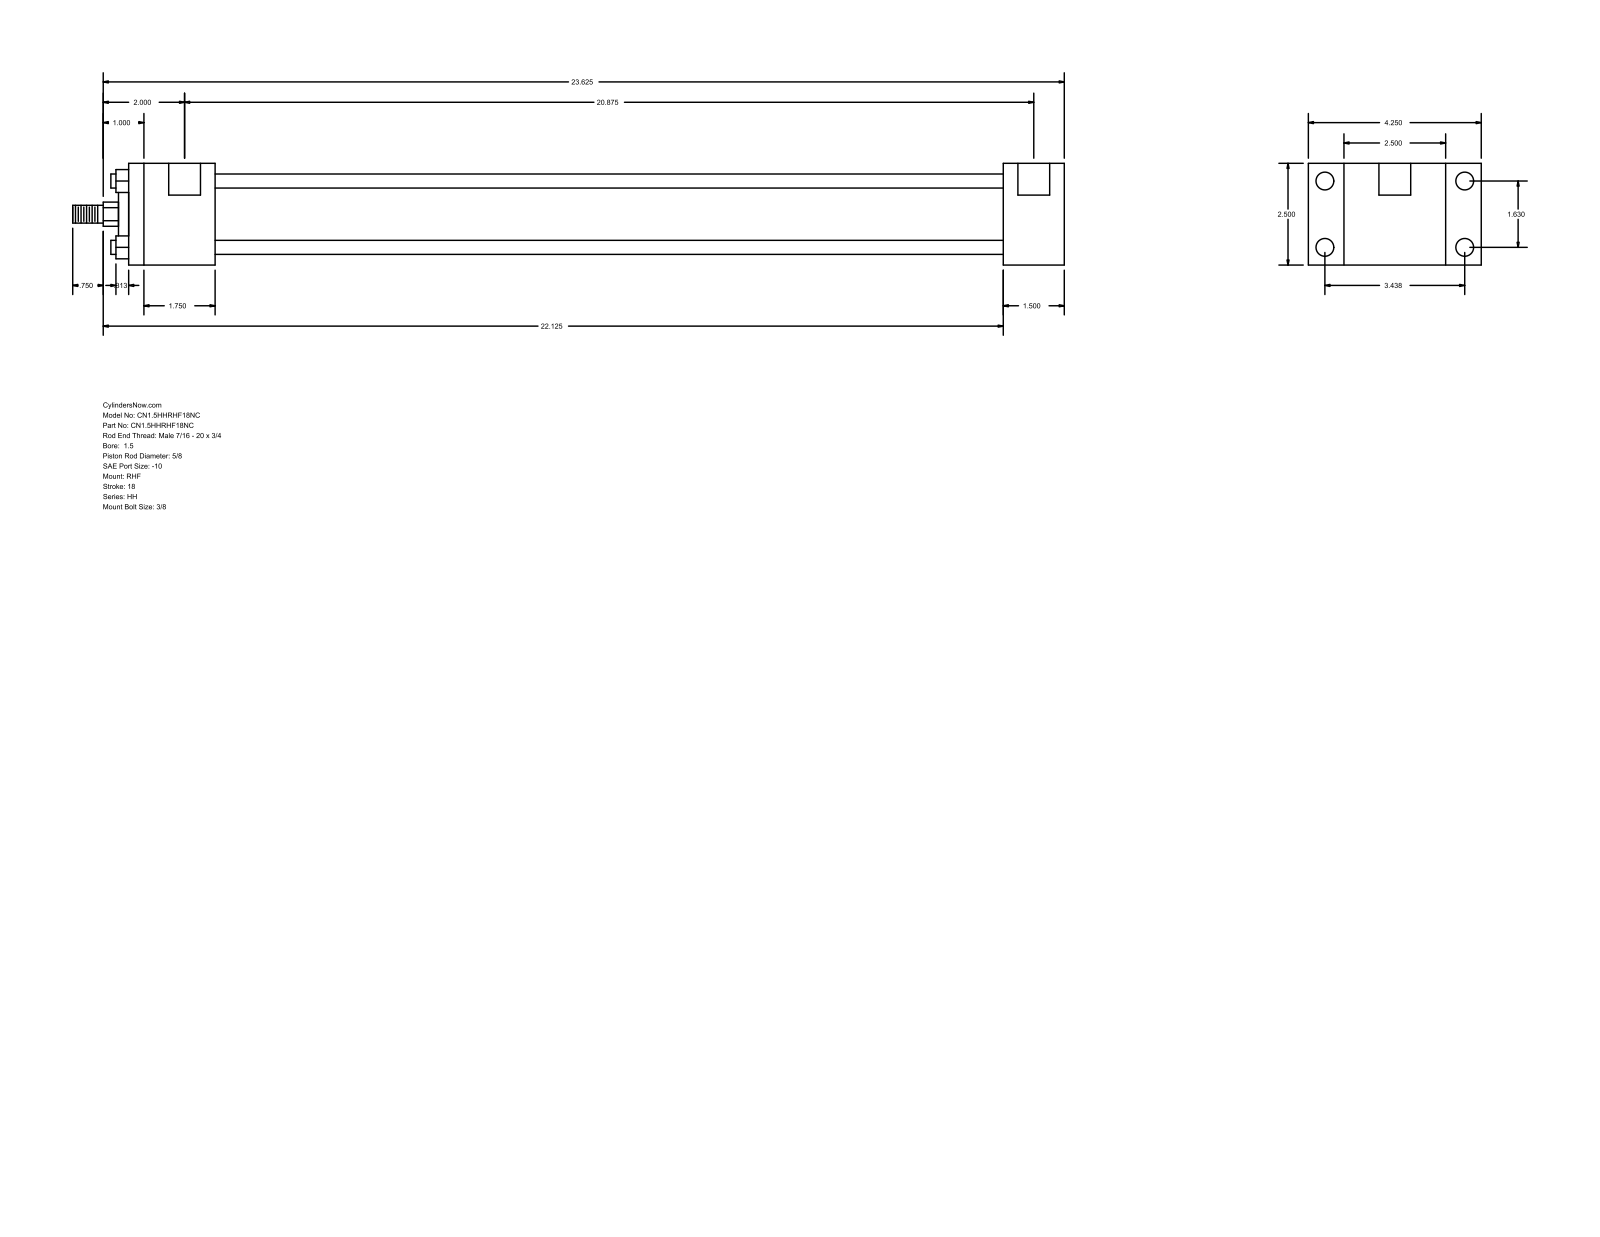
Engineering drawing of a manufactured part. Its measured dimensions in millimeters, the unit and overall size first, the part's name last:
Units: millimetres
Overall size (bounding box): 619.12 × 107.95 × 63.5
Round holes (diameter × count): ⌀5.56 ×4, ⌀11.13 ×4, ⌀19.84 ×2
Round bosses / shafts (diameter × count): ⌀8.76 ×4, ⌀44.45 ×1, ⌀28.57 ×1, ⌀15.88 ×1, ⌀11.11 ×1
Partial cylindrical surfaces — rounded edges, fillets, slot ends (radius × count): R7.54 ×1
Main face-to-face distances: 63.5, 38.1, 22.23, 85.73, 546.1, 584.2, 107.96, 53.97, 492.13, 530.23
Hole centre spacings: 1.59, 41.4, 87.32, 96.64, 531.81, 533.4, 530.22
Bodies: 0 solids, 88 faces (60 planar, 28 cylindrical, 0 other)
Part name (STEP PRODUCT): HH_RHF__0150_0.625
STEP written by: GSSL Pune (CONFIG_CONTROL_DESIGN)
